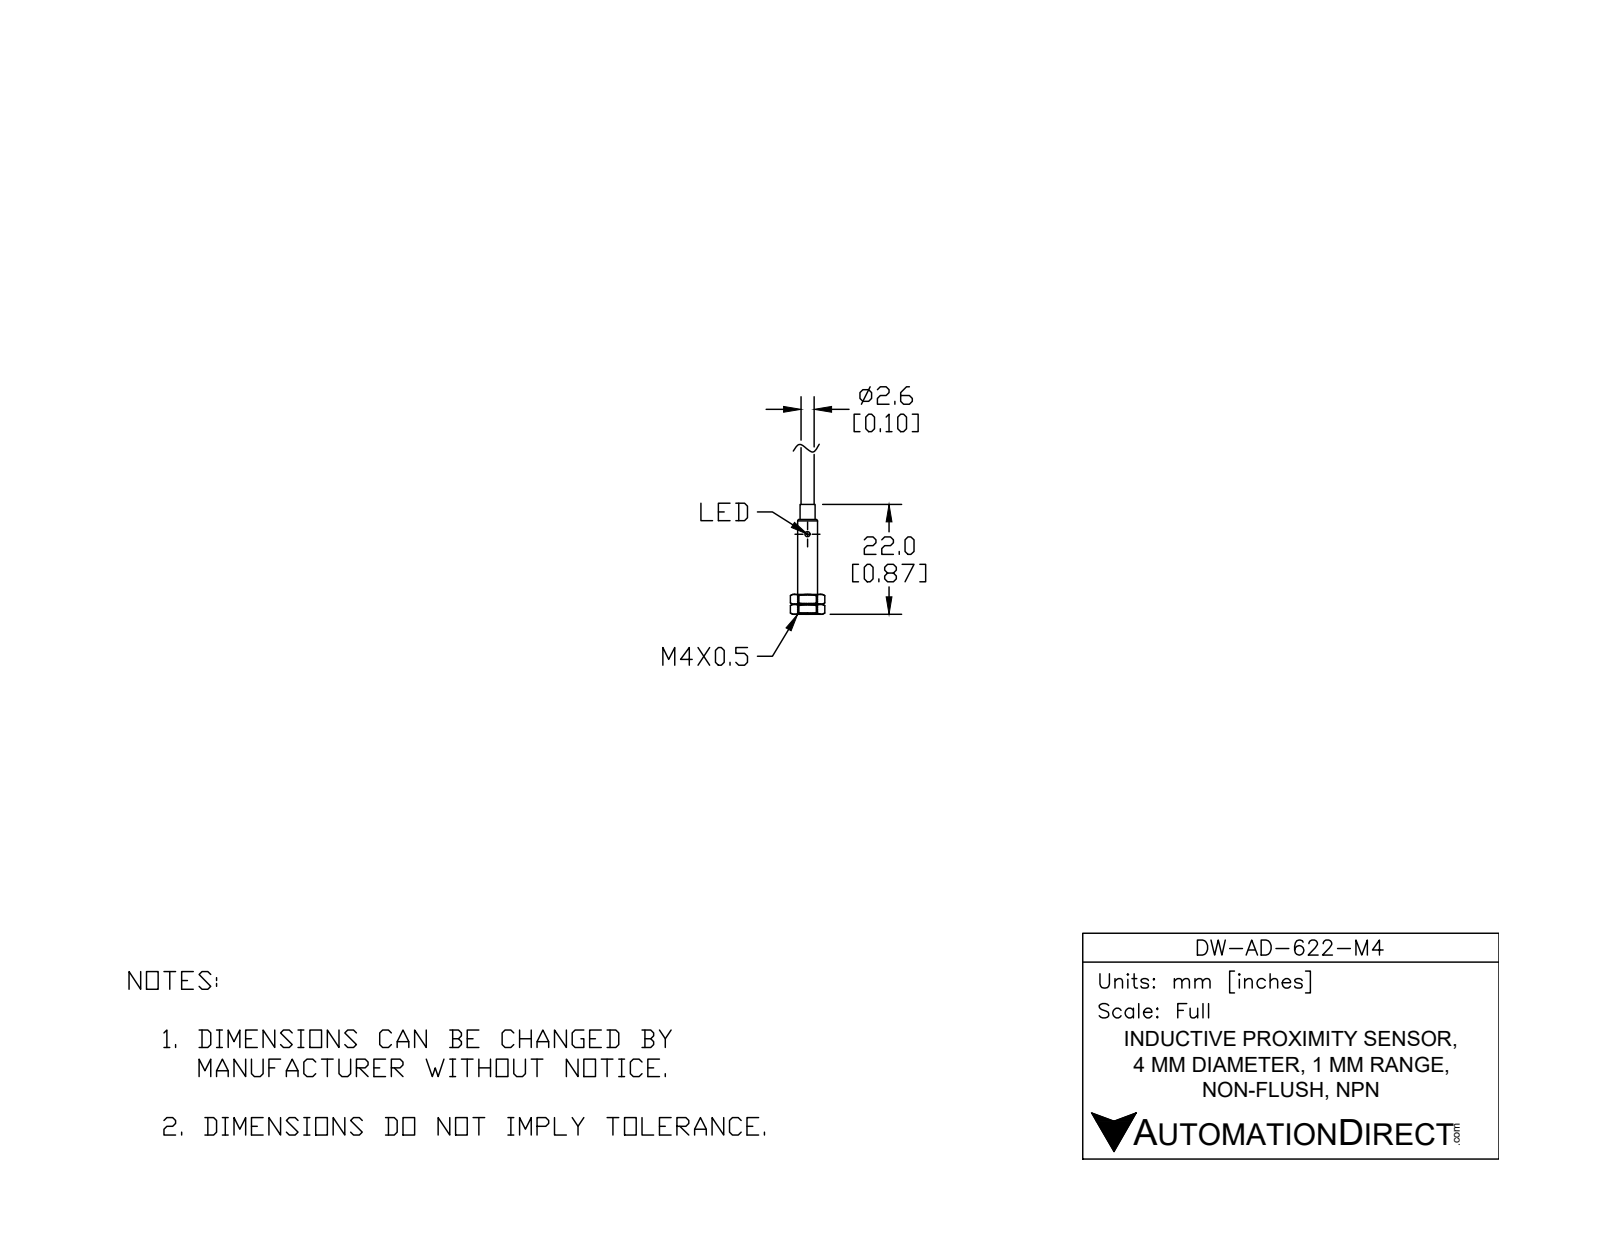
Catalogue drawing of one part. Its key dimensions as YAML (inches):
part_name: "DW-AD-622-M4"
step_written_by: "SolidWorks 2017 (AUTOMOTIVE_DESIGN)"
units: inches
bodies: {solids: 2, faces: 14, planar: 6, cylindrical: 3, other: 5}
overall_size: [1.221, 0.157, 0.157]
volume: 0.022
surface_area: 0.704
round_bosses_or_shafts:
  - {diameter: 0.157, count: 1}
  - {diameter: 0.122, count: 1}
  - {diameter: 0.102, count: 1}
face_to_face_distances: [0.866, 0.472, 0.394]
